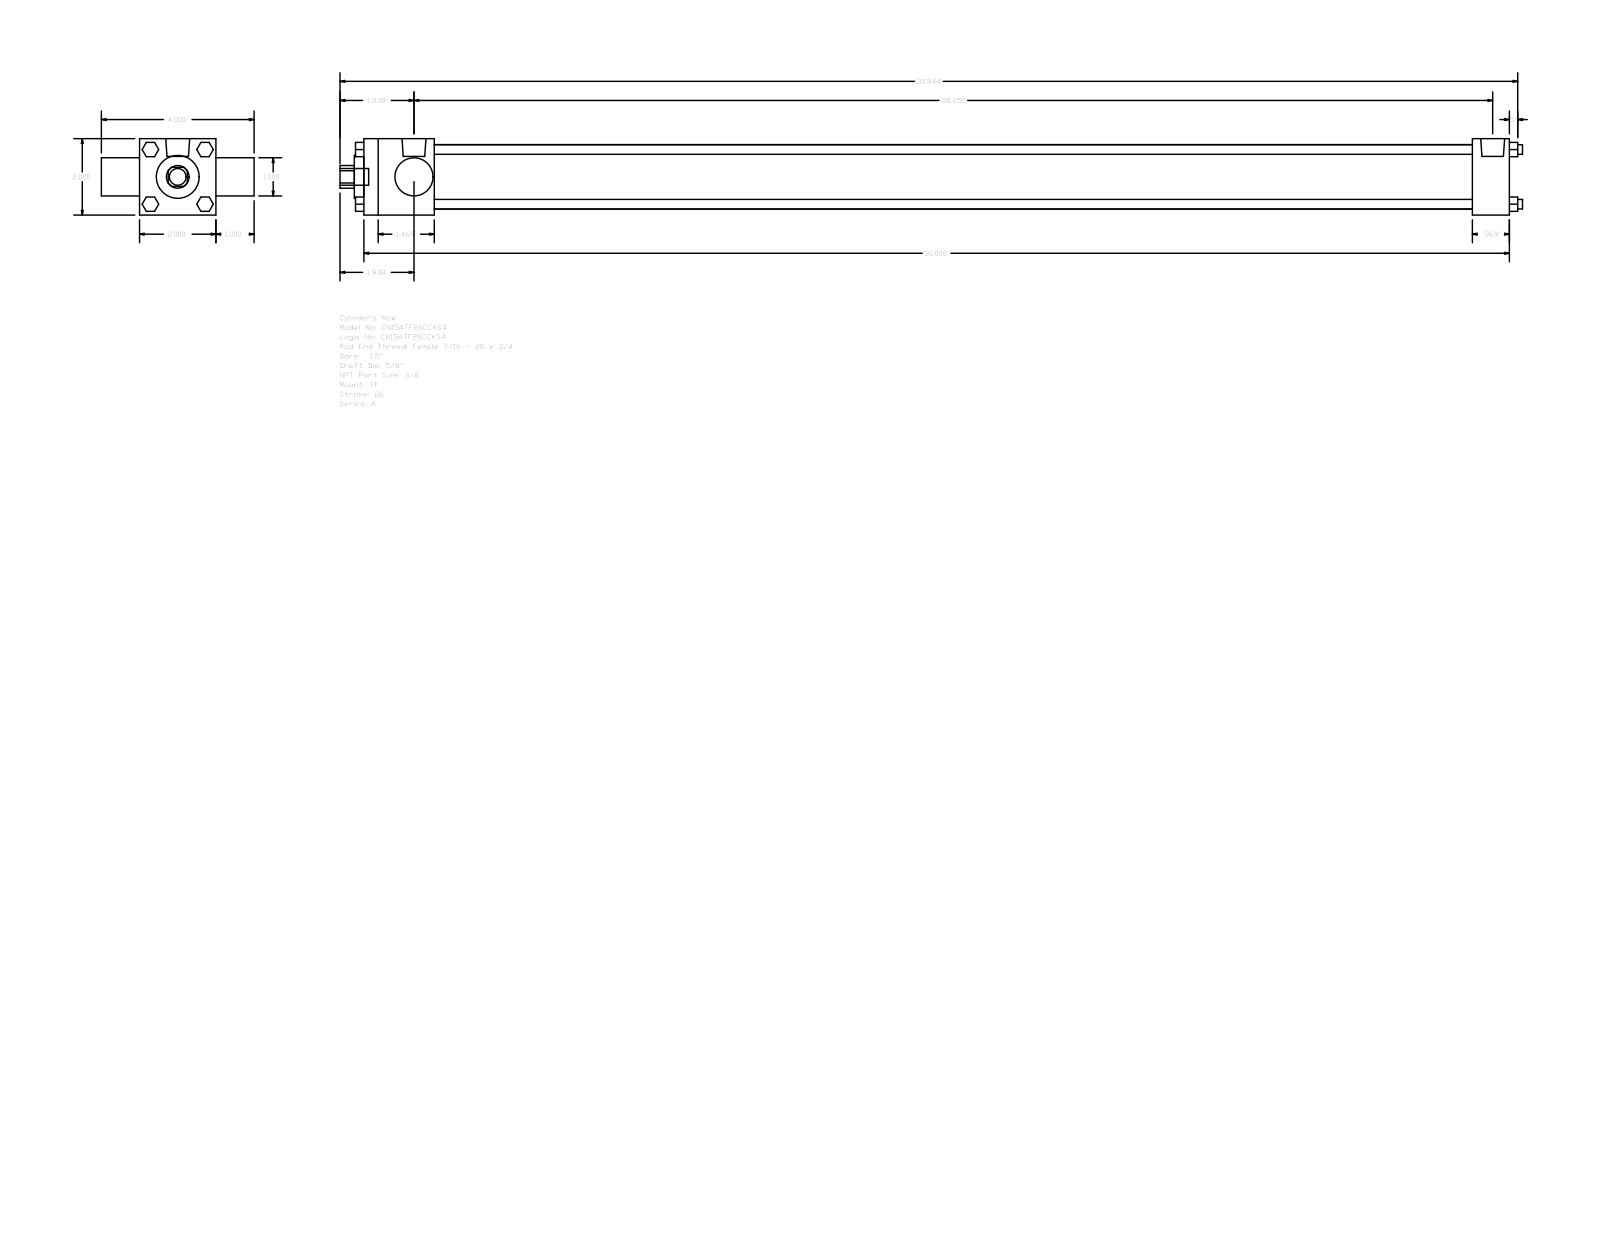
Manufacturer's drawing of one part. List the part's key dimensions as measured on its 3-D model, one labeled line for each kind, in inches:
Part name (STEP PRODUCT): A_TF__0150_0.625
STEP written by: GSSL Pune (CONFIG_CONTROL_DESIGN)
Units: inches
Bodies: 0 solids, 120 faces (92 planar, 28 cylindrical, 0 other)
Overall size (bounding box): 30.969 × 4 × 2
Round holes (diameter × count): ⌀0.625 ×1, ⌀1 ×1, ⌀1.125 ×1, ⌀1.69 ×1
Round bosses / shafts (diameter × count): ⌀0.25 ×4, ⌀0.219 ×3, ⌀0.627 ×2, ⌀0.437 ×1
Partial cylindrical surfaces — rounded edges, fillets, slot ends (radius × count): R0.297 ×1
Main face-to-face distances: 2, 30, 1, 3, 1.844, 29.031, 27.187, 28.156, 0.969, 0.375
